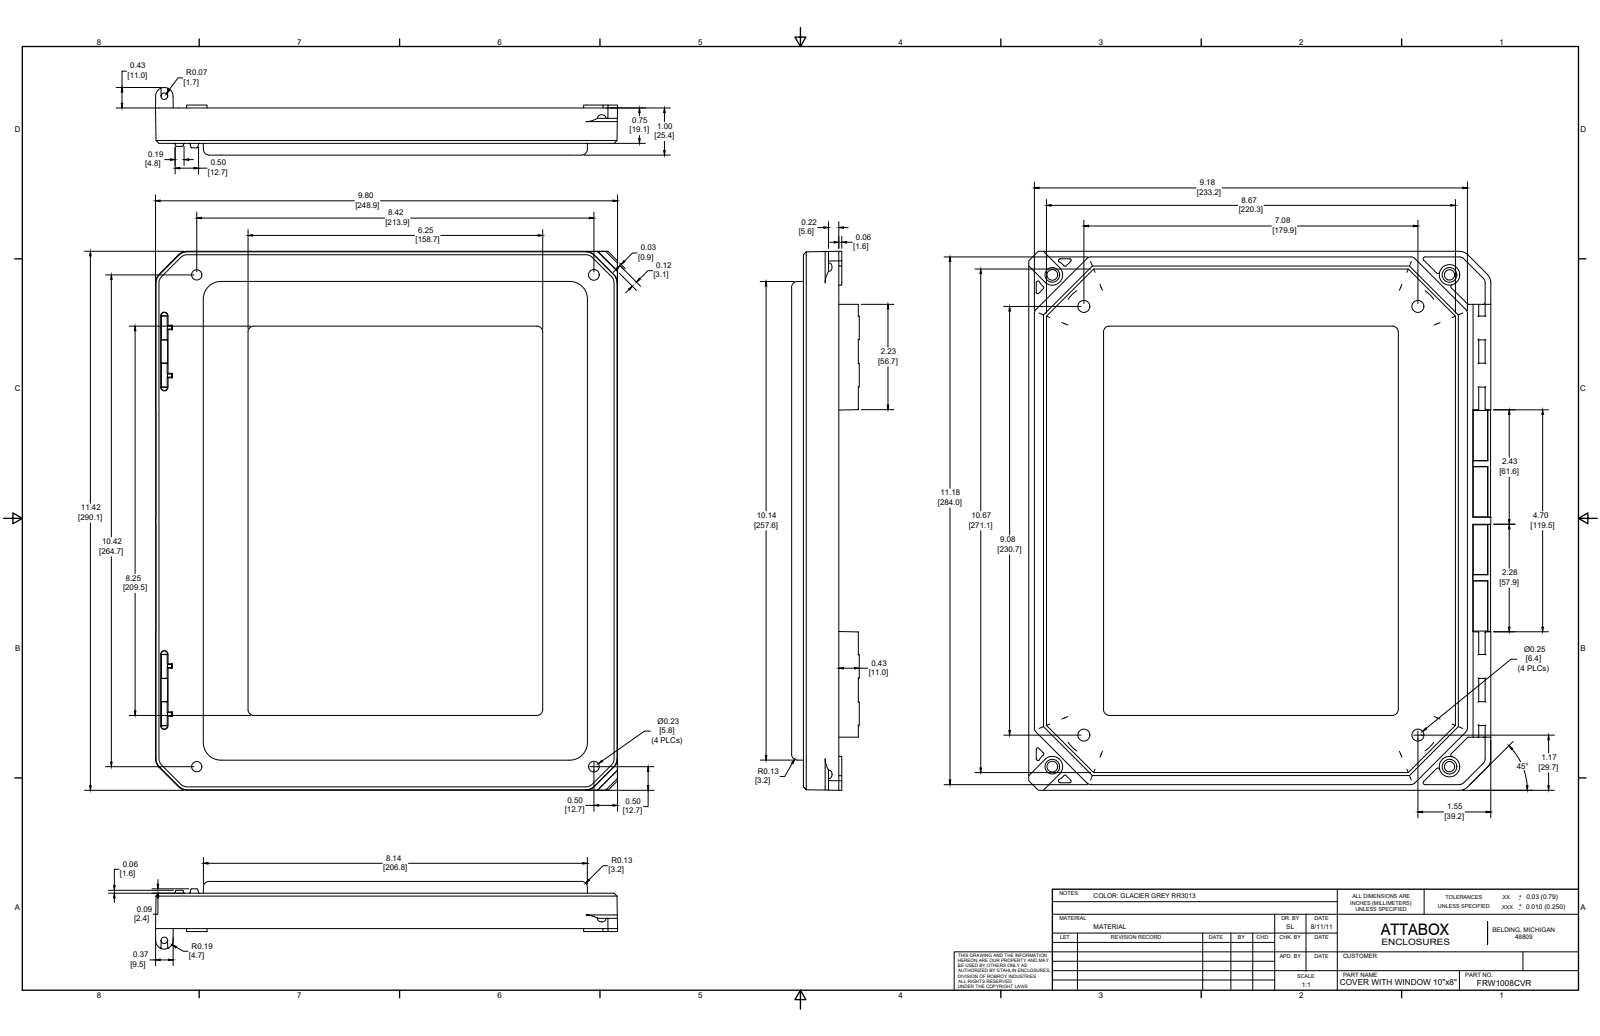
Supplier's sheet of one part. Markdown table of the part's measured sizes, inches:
| quantity | value |
| --- | --- |
| part name | FRW1008CVR |
| STEP written by | SolidWorks 2019 (AUTOMOTIVE_DESIGN) |
| units | inches |
| bodies | 1 solid, 583 faces (239 planar, 196 cylindrical, 148 other) |
| overall size | 11.423 × 9.798 × 1.434 |
| volume | 19.55 in³ |
| surface area | 222.3 in² |
| round holes (diameter × count) | 0.253 × 4, 0.219 × 2, 0.227 × 2, 0.313 × 2, 0.137 × 1 |
| round bosses / shafts (diameter × count) | 0.435 × 2 |
| partial cylindrical surfaces (radius × count) | 0.03 × 27, 0.062 × 16, 0.096 × 16, 0.125 × 16, 0.01 × 14, 0.06 × 11, 0.04 × 10, 0.02 × 8 |
| main face-to-face distances | 0.125, 0.25, 0.125, 0.75, 0.375, 0.375, 1, 0.625, 0.875, 0.625 |
| hole center spacings | 9.776, 0.946, 0.947, 7.084, 7.781, 7.783, 8.423, 9.084 |
